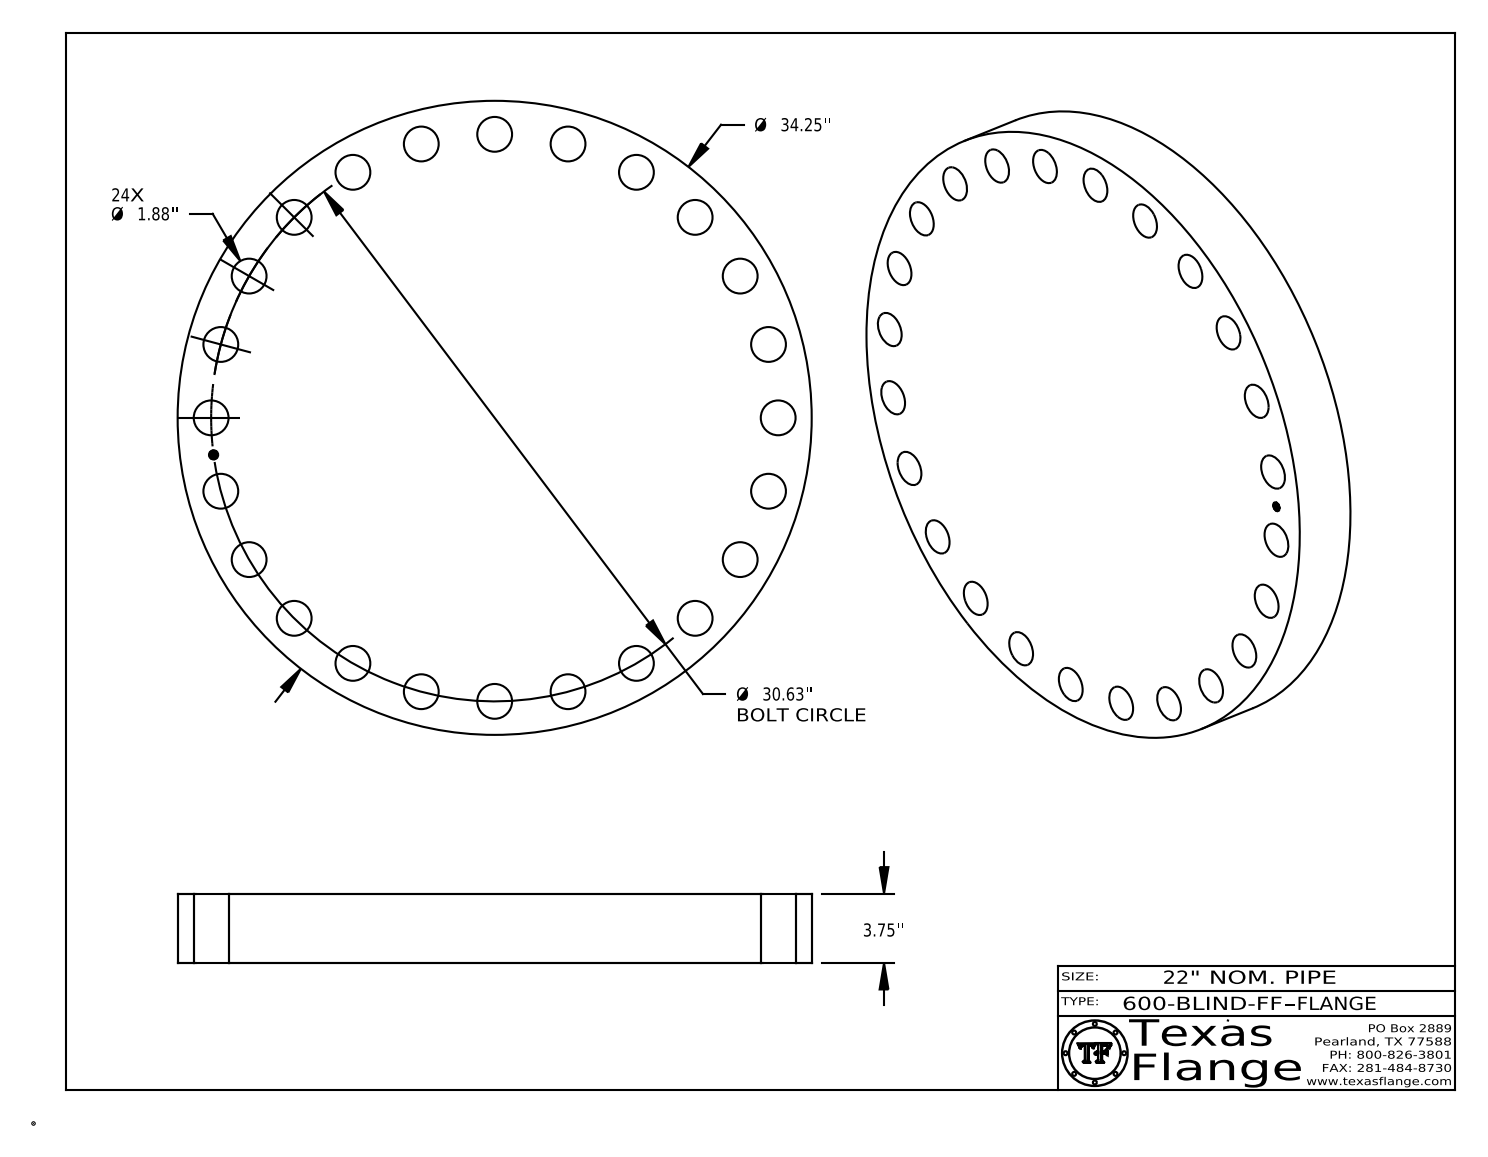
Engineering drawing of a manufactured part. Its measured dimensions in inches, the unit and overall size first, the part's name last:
Units: inches
Overall size (bounding box): 34.25 × 34.25 × 3.75
Round holes (diameter × count): ⌀1.88 ×24, ⌀0.495 ×1
Round bosses / shafts (diameter × count): ⌀0.03 ×8, ⌀34.25 ×1, ⌀0.39 ×1
Main face-to-face distances: 3.75, 0.015, 3.735, 0.148, 0.145, 0.027, 0.096, 0.123, 0.022, 0.074
Hole centre spacings: 3.998, 11.722, 24.3, 15.315, 7.928, 18.646, 28.298, 30.368
Volume: 3 205 in³ · Surface area: 2 645 in²
Bodies: 1 solid, 437 faces (367 planar, 70 cylindrical, 0 other)
Part name (STEP PRODUCT): 600-BLIND-FF
STEP written by: CATIA V5 STEP AP214 (AUTOMOTIVE_DESIGN)
